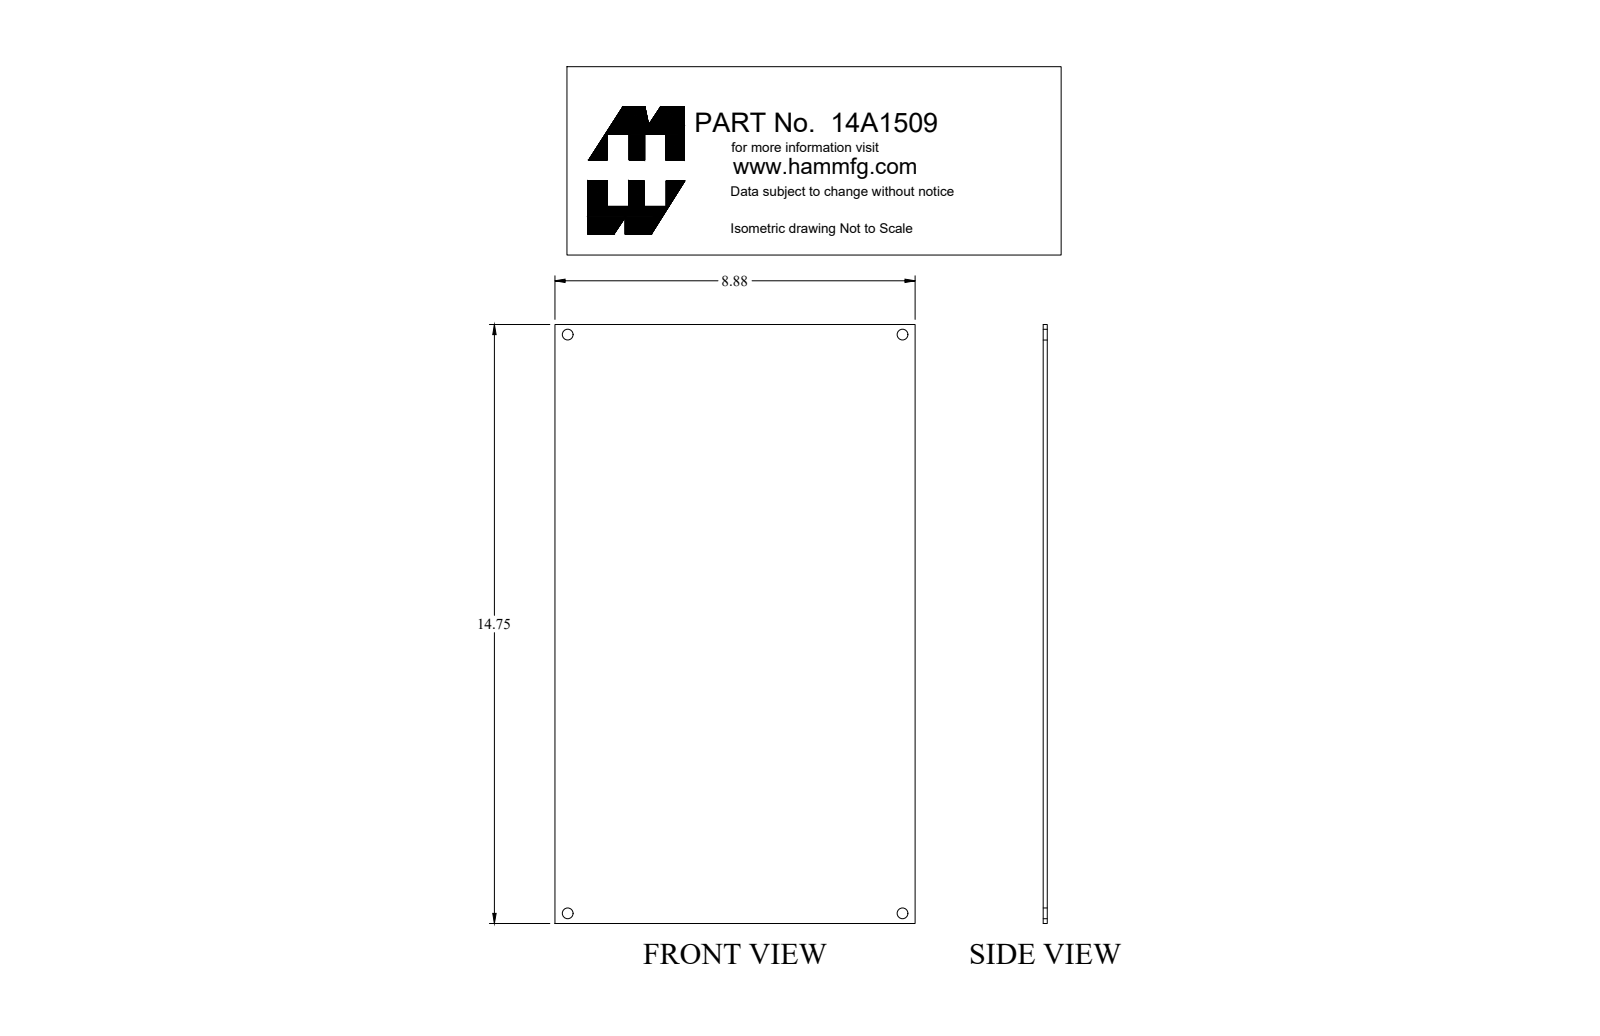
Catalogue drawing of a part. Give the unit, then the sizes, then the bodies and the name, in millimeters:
Units: millimetres
Overall size (bounding box): 374.7 × 225.4 × 2.5
Round holes (diameter × count): ⌀6.7 ×4
Main face-to-face distances: 2.5, 225.4, 374.7
Hole centre spacings: 209.6, 362, 418.2
Volume: 214 200 mm³ · Surface area: 171 900 mm²
Bodies: 1 solid, 10 faces (6 planar, 4 cylindrical, 0 other)
Part name (STEP PRODUCT): 14A1509
STEP written by: SolidWorks 2018 (AUTOMOTIVE_DESIGN)
